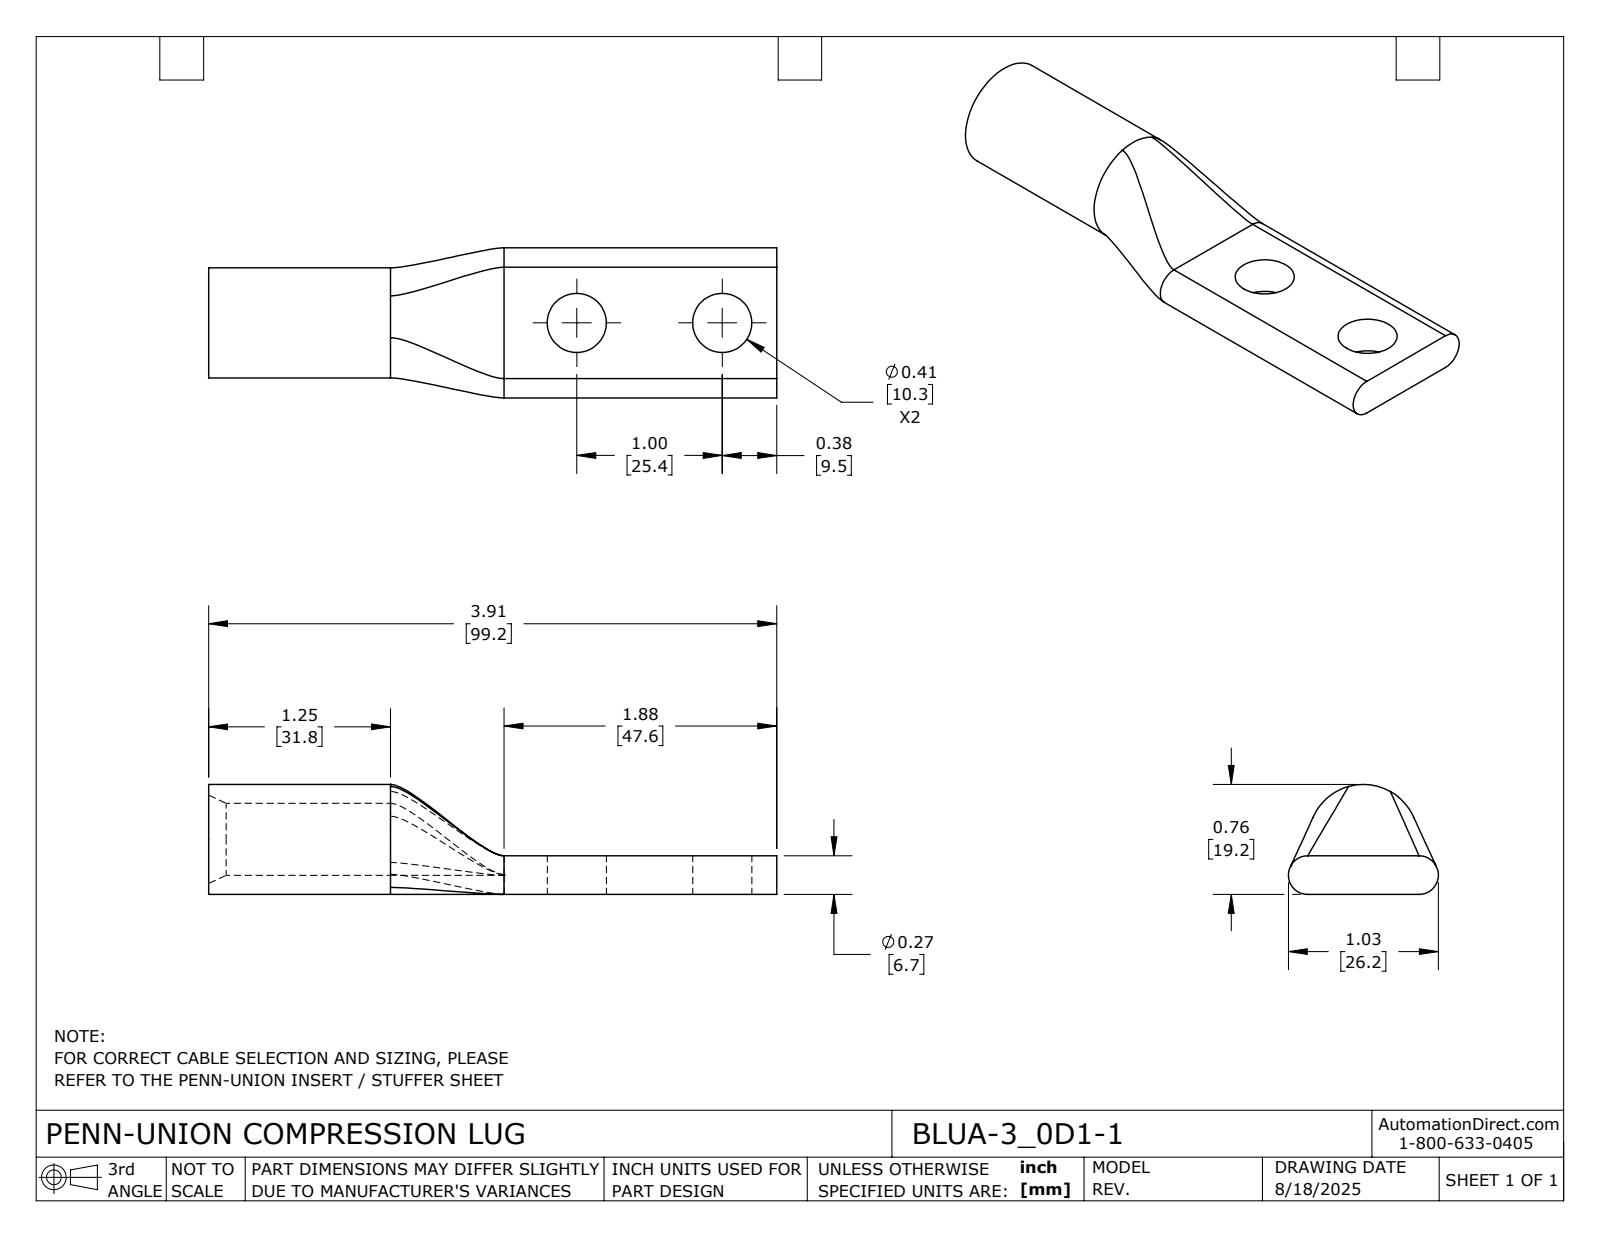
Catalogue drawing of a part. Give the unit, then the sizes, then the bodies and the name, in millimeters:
Units: millimetres
Overall size (bounding box): 99.2 × 26.2 × 19.2
Round holes (diameter × count): ⌀10.3 ×2, ⌀12.6 ×1
Round bosses / shafts (diameter × count): ⌀19.2 ×1
Partial cylindrical surfaces — rounded edges, fillets, slot ends (radius × count): R3.4 ×2
Main face-to-face distances: 6.8, 99.2, 51.6, 47.6
Hole centre spacings: 25.4
Volume: 15 300 mm³ · Surface area: 8 503 mm²
Bodies: 1 solid, 26 faces (5 planar, 11 cylindrical, 10 other)
Part name (STEP PRODUCT): BLUA-3_0D1-1
STEP written by: SolidWorks 2024 (CONFIG_CONTROL_DESIGN)
